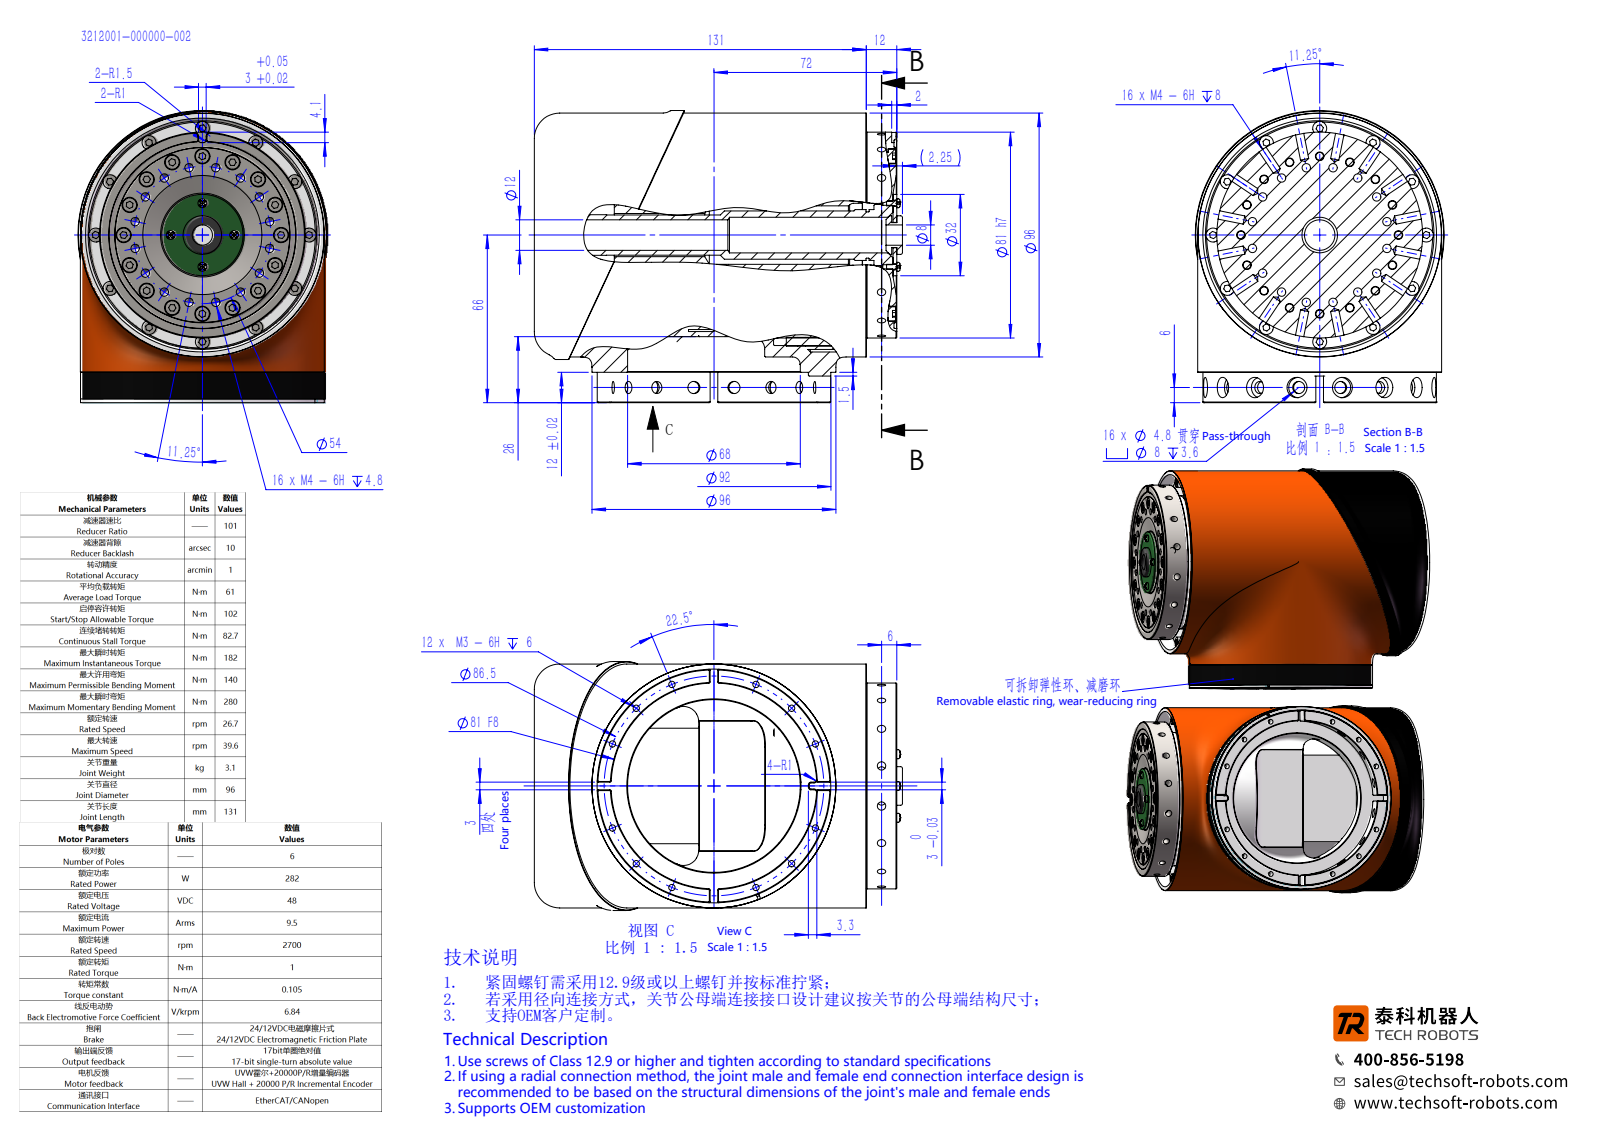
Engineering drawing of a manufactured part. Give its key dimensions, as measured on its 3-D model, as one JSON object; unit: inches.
{"step_written_by": "SolidWorks 2016 (CONFIG_CONTROL_DESIGN)", "units": "inches", "bodies": {"solids": 23, "faces": 1769, "planar": 592, "cylindrical": 705, "other": 472}, "overall_size": [5.708, 4.528, 3.858], "volume_in3": 62.24, "surface_area_in2": 186.5, "round_holes": [[0.098, 44], [0.13, 32], [0.138, 32], [0.134, 23], [0.236, 20], [0.315, 17], [0.189, 16], [0.063, 4], [0.094, 4], [0.276, 3], [0.394, 1], [0.472, 1]], "round_bosses_or_shafts": [[0.217, 32], [0.118, 32], [0.138, 4], [0.079, 4], [3.858, 1], [3.781, 1], [3.78, 1], [3.622, 1]], "partial_cylinders_radius": [[0.02, 16], [0.039, 8], [0.059, 2], [0.236, 2], [0.197, 1], [1.108, 1], [1.772, 1]], "face_to_face_distances": [0.472, 4.891, 0.551, 0.256, 5.147, 0.728, 5.62, 0.465, 0.72, 5.612], "hole_center_spacings": [1.768, 2.185, 2.272, 0.273, 1.063, 2.085, 0.68, 1.181]}
